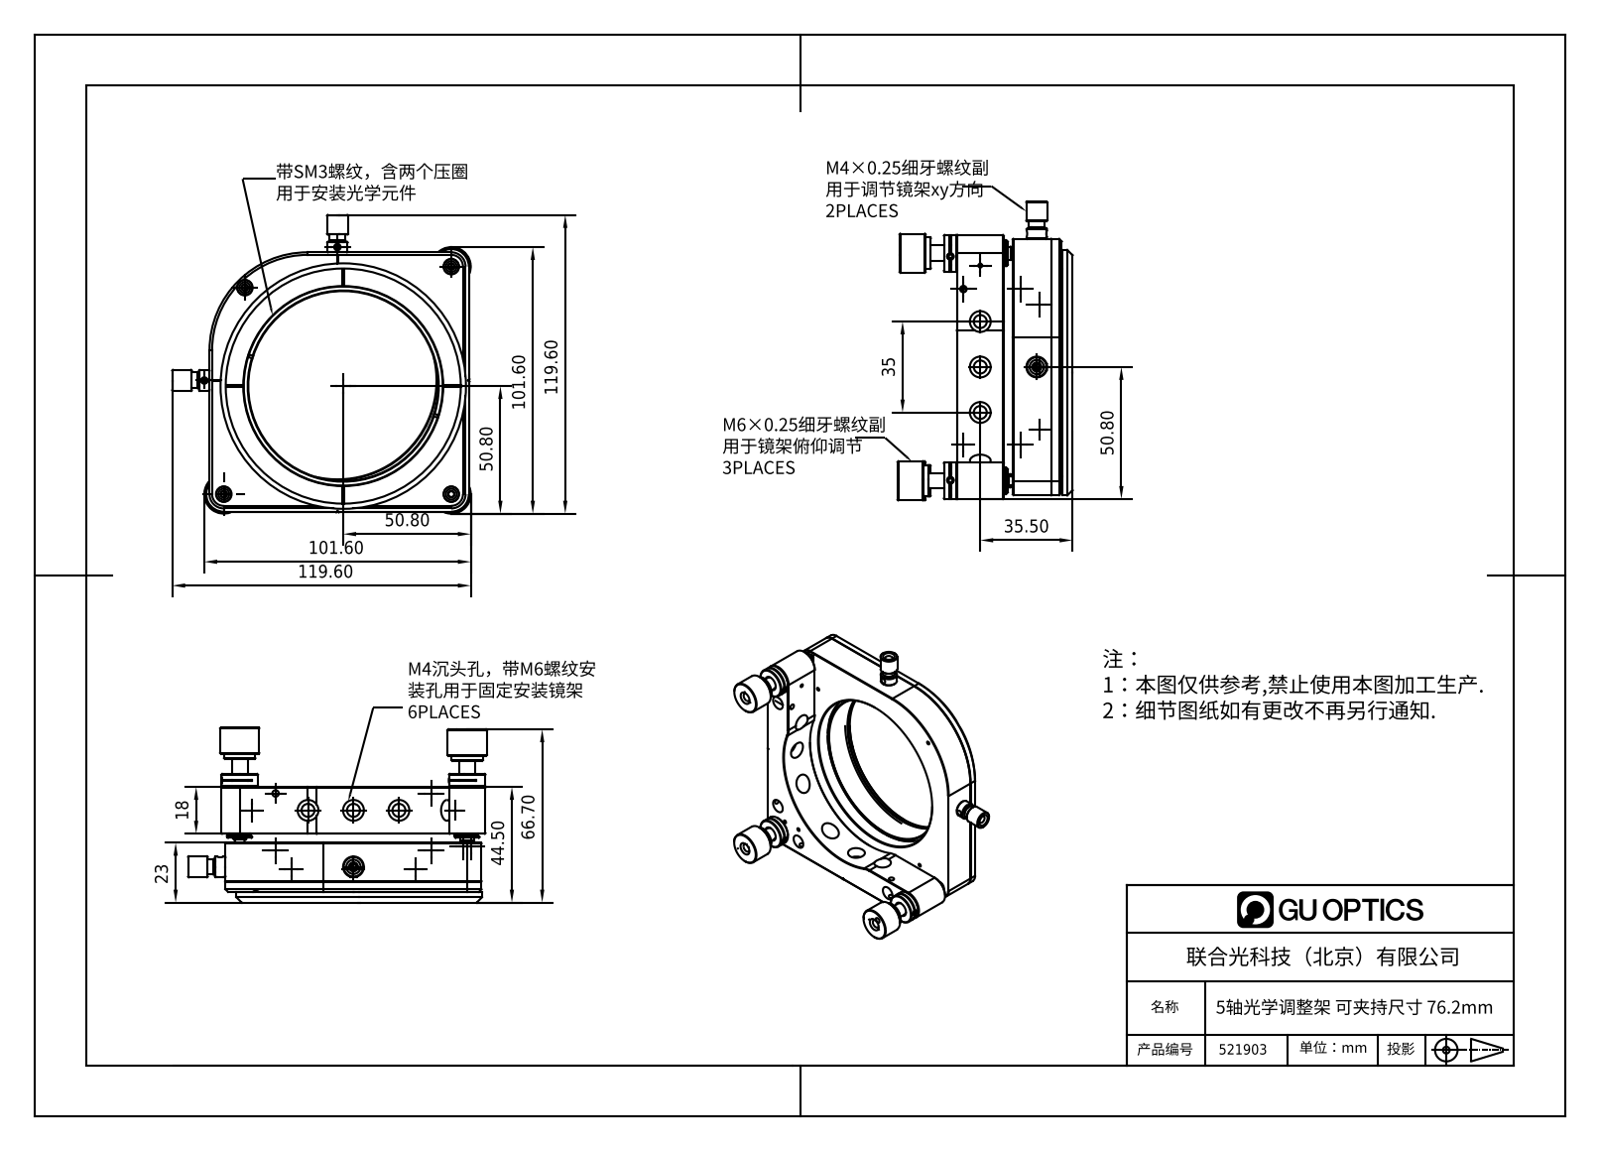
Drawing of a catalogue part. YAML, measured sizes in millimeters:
part_name: "5轴光学调整架 可夹持尺寸76.2mm"
step_written_by: "SolidWorks 2020 (CONFIG_CONTROL_DESIGN)"
units: millimeters
bodies: {solids: 48, faces: 1509, planar: 501, cylindrical: 564, other: 444}
overall_size: [114.94, 114.94, 68.66]
volume: 135527
surface_area: 84324
round_holes:
  - {diameter: 2.5, count: 20}
  - {diameter: 1.5, count: 12}
  - {diameter: 6.5, count: 7}
  - {diameter: 5, count: 6}
  - {diameter: 6.2, count: 6}
  - {diameter: 8, count: 6}
  - {diameter: 2.05, count: 4}
  - {diameter: 3.4, count: 4}
  - {diameter: 6, count: 4}
  - {diameter: 1.8, count: 3}
  - {diameter: 3.99, count: 3}
  - {diameter: 4, count: 3}
round_bosses_or_shafts:
  - {diameter: 3, count: 11}
  - {diameter: 8, count: 5}
  - {diameter: 15, count: 3}
  - {diameter: 14, count: 3}
  - {diameter: 12, count: 3}
  - {diameter: 9.5, count: 3}
  - {diameter: 5, count: 3}
  - {diameter: 7.8, count: 2}
partial_cylinders:
  - {radius: 0.2, count: 36}
  - {radius: 0.75, count: 12}
  - {radius: 1.5, count: 12}
  - {radius: 10, count: 10}
  - {radius: 1, count: 8}
  - {radius: 0.5, count: 6}
  - {radius: 3, count: 6}
  - {radius: 0.78, count: 4}
face_to_face_distances: [15, 4, 8.5, 6.5, 3.9, 10, 18.9, 12.4, 1, 1.5]
hole_center_spacings: [60, 99.72, 97.23, 3.83, 5.28, 5.5, 9.41, 13.8]
